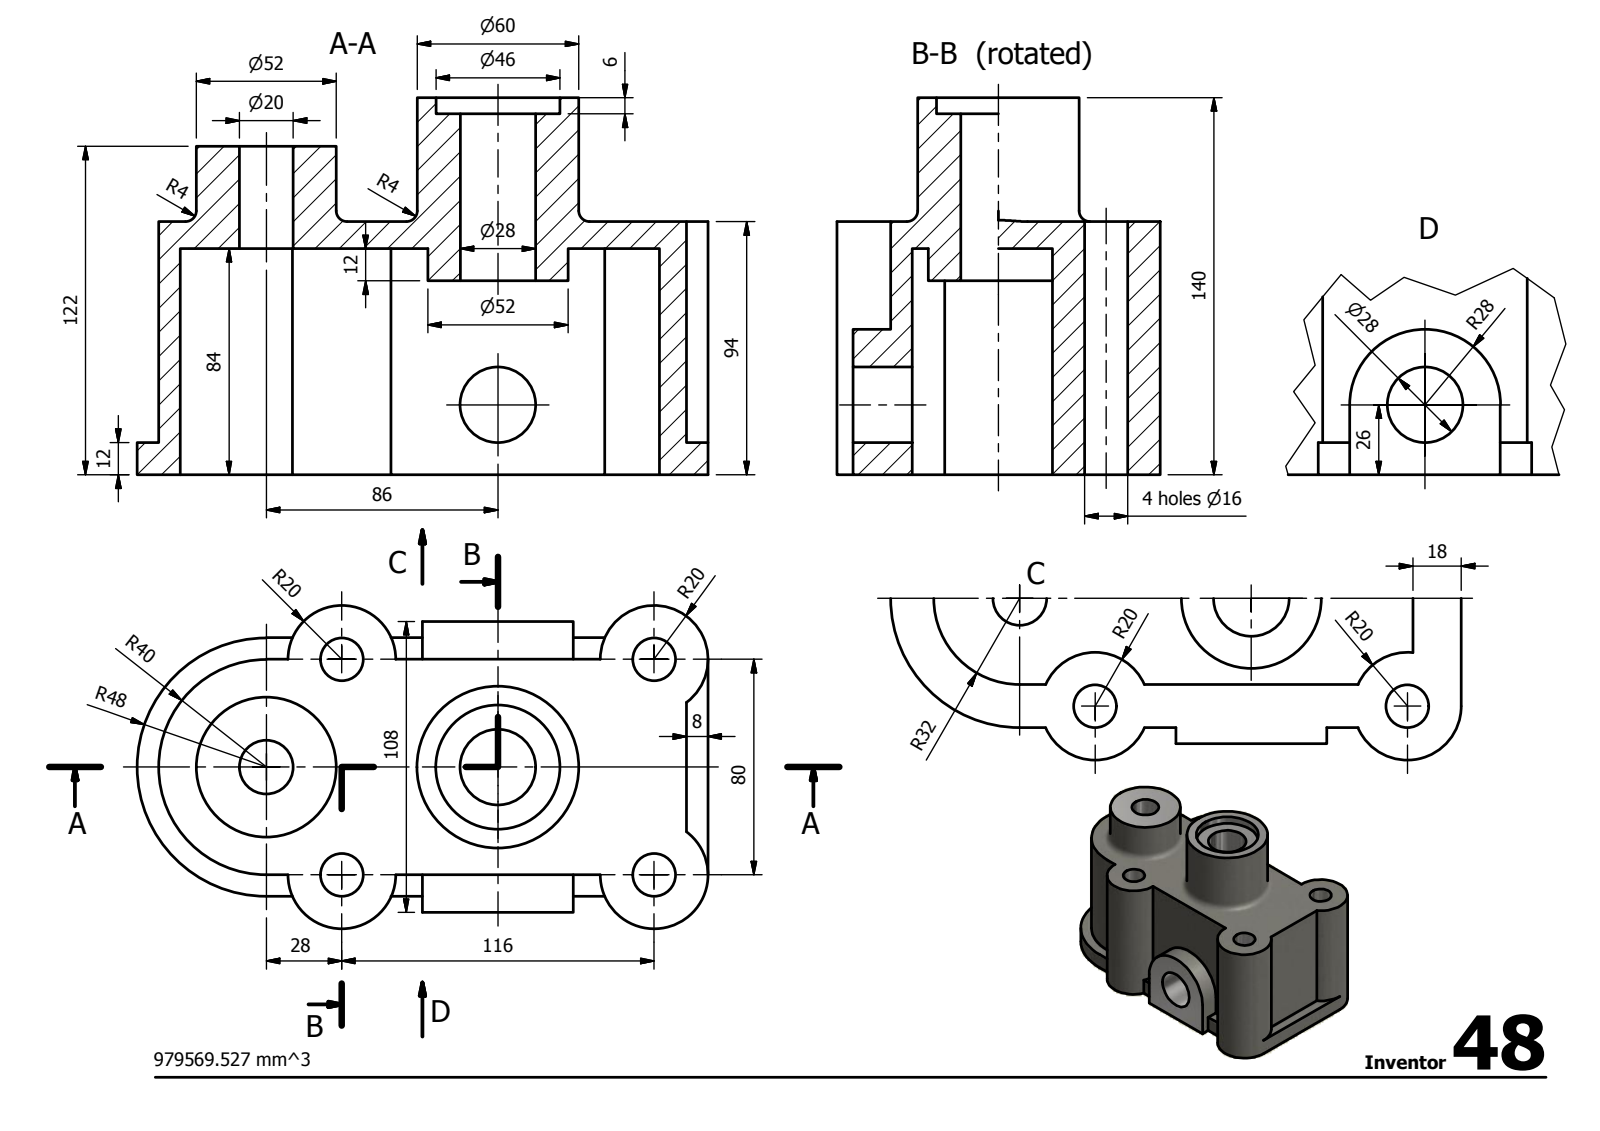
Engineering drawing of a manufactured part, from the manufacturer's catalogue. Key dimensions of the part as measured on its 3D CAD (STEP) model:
STEP written by: Autodesk Inventor 2014 (AUTOMOTIVE_DESIGN)
Units: millimetres
Bodies: 1 solid, 63 faces (36 planar, 25 cylindrical, 2 other)
Overall size (bounding box): 212 × 140 × 120
Volume: 979 570 mm³ · Surface area: 182 512 mm²
Round holes (diameter × count): ⌀16 ×4, ⌀28 ×2, ⌀20 ×1, ⌀46 ×1
Round bosses / shafts (diameter × count): ⌀40 ×4, ⌀52 ×2, ⌀60 ×1
Partial cylindrical surfaces — rounded edges, fillets, slot ends (radius × count): R28 ×1, R32 ×1, R40 ×1, R48 ×1
Main face-to-face distances: 94, 72, 8, 10, 84, 64, 80, 22, 12, 14
Hole centre spacings: 70.46, 48.83, 80, 116, 140.91, 149.45, 86
